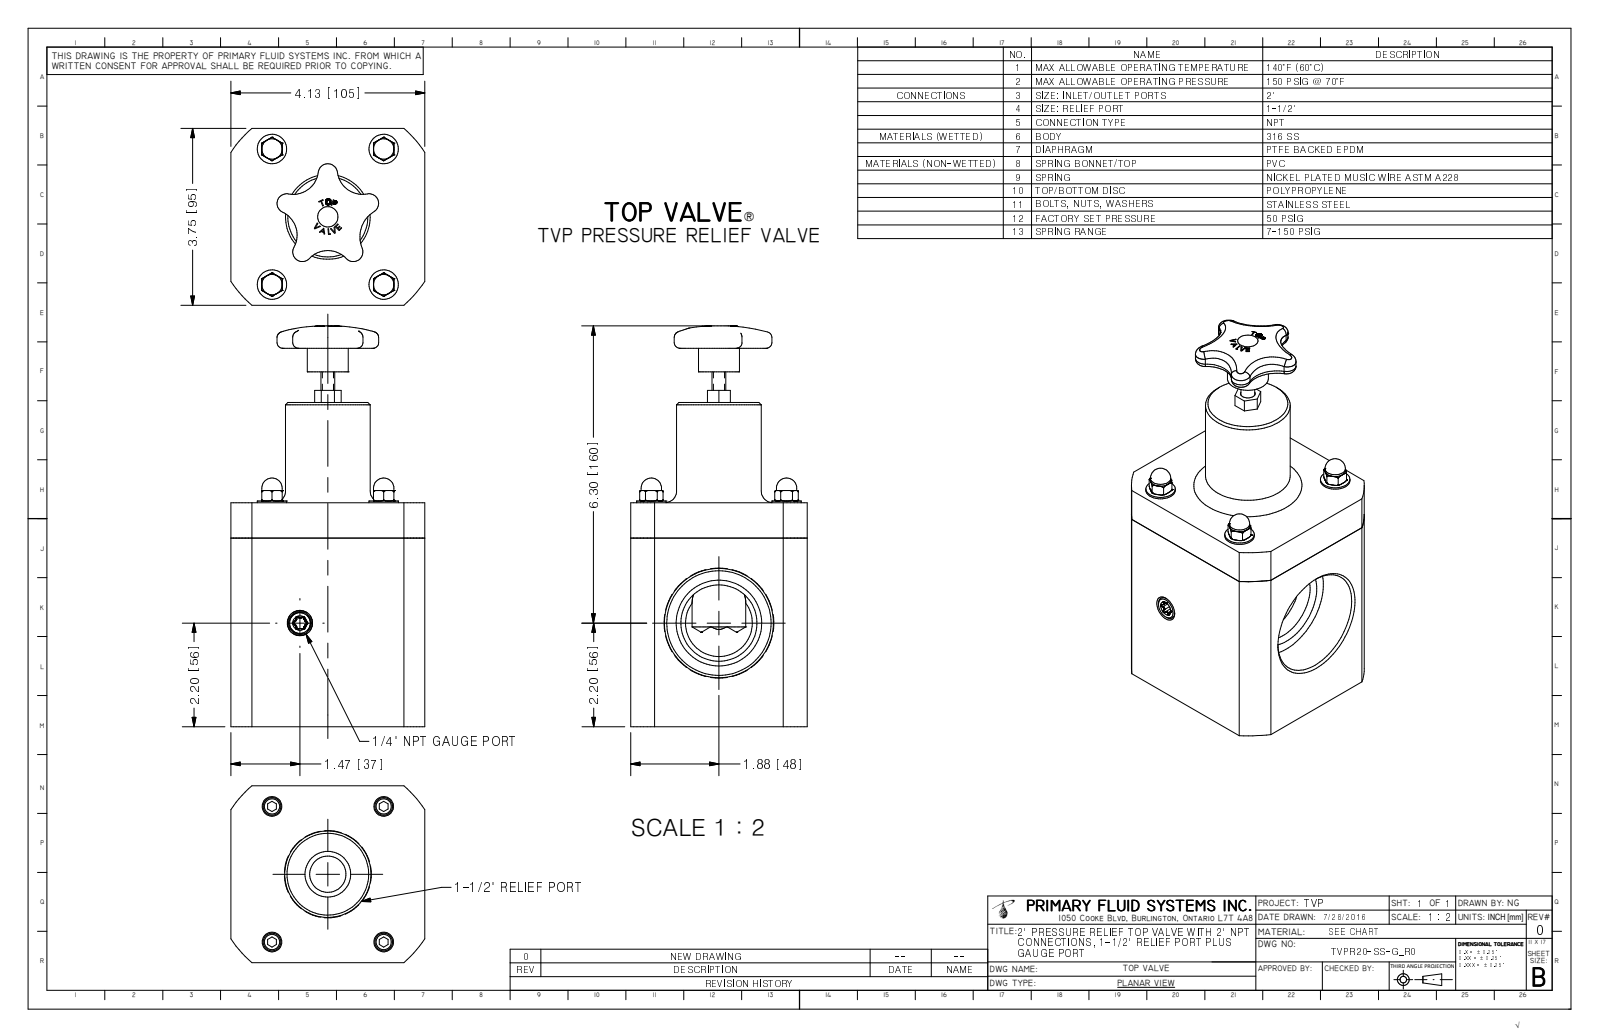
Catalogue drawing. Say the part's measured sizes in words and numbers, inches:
The part is named "TVPR20-SS-G_R0". Its 3-D file was written by "Autodesk Inventor 2009 (AUTOMOTIVE_DESIGN)". It is 1 solid with 362 faces: 153 planar, 52 cylindrical and 157 other. Overall it measures 8.5 by 4.125 by 3.75 inches. Its volume is 69.91 cubic inches and its surface area 144 square inches. Round holes: 4 of diameter 0.175, 1 of diameter 1.734, 1 of diameter 2.219. Round bosses or shafts: 4 of diameter 0.625, 4 of diameter 0.433, 4 of diameter 0.375, 1 of diameter 1.8, 1 of diameter 0.87, 1 of diameter 0.293. Partial cylindrical surfaces (rounded edges, fillets, slot ends): 6 of radius 0.027, 5 of radius 0.085, 5 of radius 0.205, 4 of radius 0.536, 4 of radius 0.656, 1 of radius 0.625, 1 of radius 0.745, 1 of radius 2.475. The main face-to-face distances are 3.75, 4.75, 4.125, 0.9, 3.225, 2.325, 0.6, 4.15, 6.875, 6.275. The hole center spacings are 1.864, 1.865, 2.375, 2.875, 3.729.
